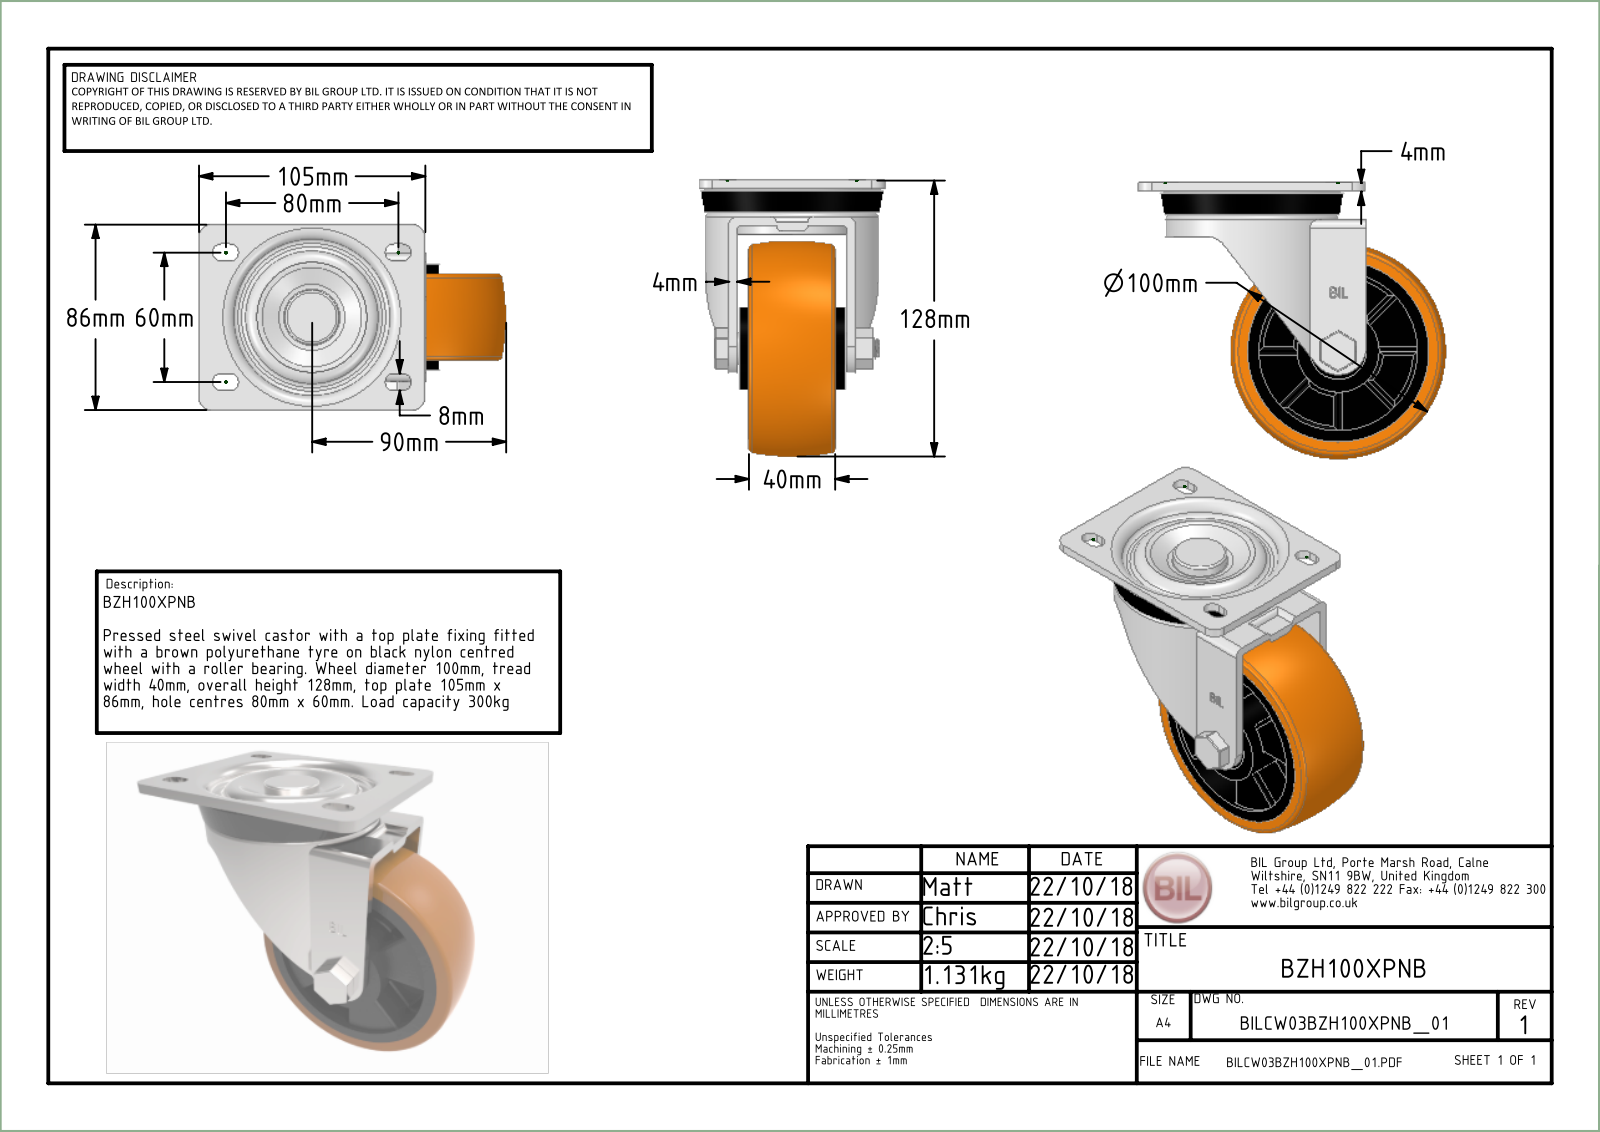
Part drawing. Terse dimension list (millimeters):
name: BZH100XPNB v3; BZH100AS - 2 v1; ZINC PLATED, PRESSED STEEL TOP PLATE (1); ZINC PLATED, PRESSED STEEL FORKS (1) (+8 more)
written by: Autodesk Translation Framework v14.10.0.0 (AUTOMOTIVE_DESIGN)
unit: mm
bodies: 19 solids, 676 faces (255 planar, 151 cylindrical, 270 other)
size: 142.5 × 128 × 86
volume: 355 281 mm³; area: 149 162 mm²
holes: 1× ⌀10, 1× ⌀10.2, 1× ⌀10.3, 1× ⌀12, 1× ⌀15, 1× ⌀15.5, 1× ⌀25, 1× ⌀26, 1× ⌀27, 1× ⌀32, 1× ⌀72, 1× ⌀73
bosses: 8× ⌀4, 1× ⌀80, 1× ⌀50.5, 1× ⌀37, 1× ⌀31, 1× ⌀26.9, 1× ⌀22.5, 1× ⌀20
rounds: 18× R0.5, 8× R4.5, 6× R0.75, 4× R2, 4× R8, 2× R4, 2× R25.41, 1× R9.25
face distances: 4, 5, 9.5, 11.5, 7.5, 5.5, 10.5, 44.5, 1, 49.5
